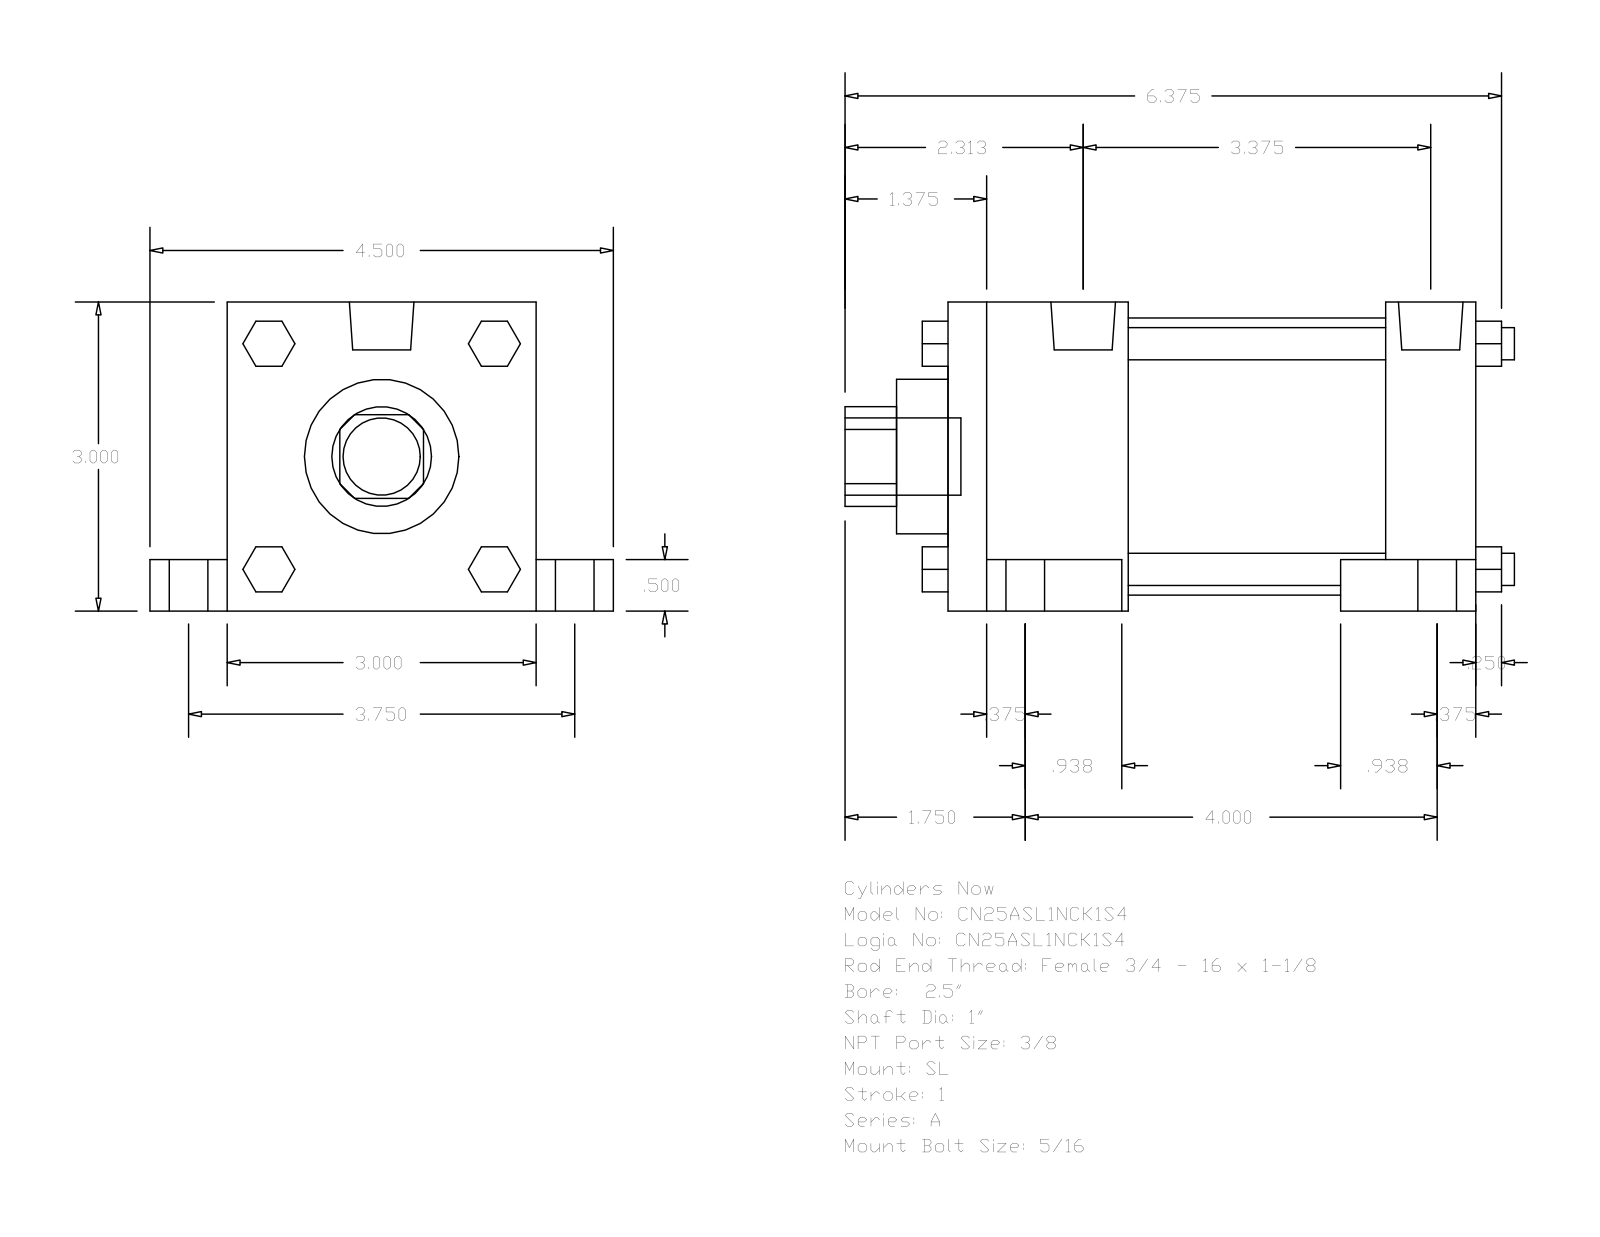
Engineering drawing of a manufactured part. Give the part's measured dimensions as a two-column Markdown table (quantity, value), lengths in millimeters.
| quantity | value |
| --- | --- |
| part name | A_SL__0250_1 |
| STEP written by | GSSL Pune (CONFIG_CONTROL_DESIGN) |
| units | millimeters |
| bodies | 0 solids, 148 faces (112 planar, 36 cylindrical, 0 other) |
| overall size | 165.1 × 114.3 × 76.2 |
| round holes (diameter × count) | 25.4 × 1, 38.1 × 1, 68.33 × 1 |
| round bosses / shafts (diameter × count) | 15.88 × 4, 9.53 × 4, 7.94 × 4, 5.56 × 4, 15.93 × 2, 19.05 × 1 |
| partial cylindrical surfaces (radius × count) | 12.29 × 1 |
| main face-to-face distances | 76.2, 130.17, 63.5, 12.7, 22.22, 44.45, 85.72, 107.95, 95.25, 19.05 |
